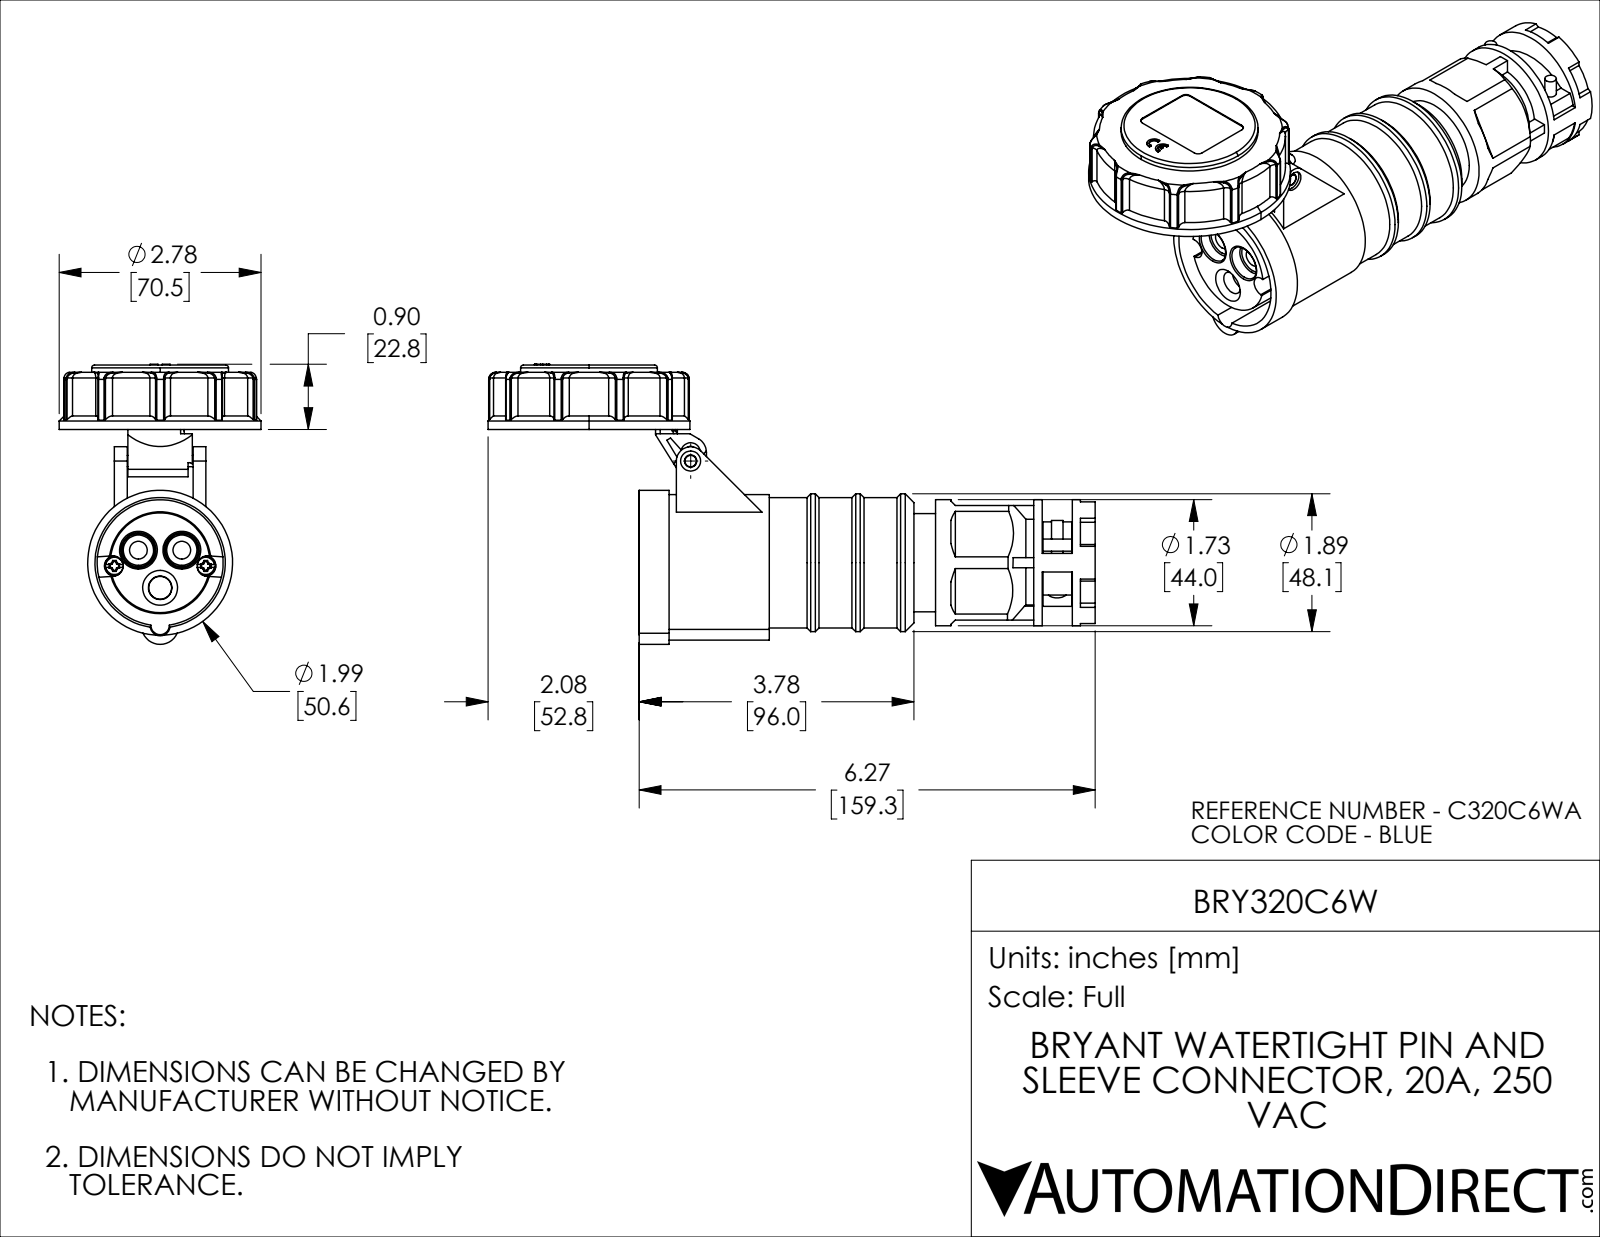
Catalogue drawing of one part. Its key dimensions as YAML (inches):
part_name: "BRY320C6W"
step_written_by: "SolidWorks 2021 (CONFIG_CONTROL_DESIGN)"
units: inches
bodies: {solids: 9, faces: 676, planar: 261, cylindrical: 247, other: 168}
overall_size: [8.349, 3.85, 2.776]
volume: 16.64
surface_area: 112.8
round_holes:
  - {diameter: 0.157, count: 2}
  - {diameter: 0.244, count: 2}
  - {diameter: 0.295, count: 2}
  - {diameter: 0.169, count: 1}
  - {diameter: 0.276, count: 1}
  - {diameter: 0.323, count: 1}
  - {diameter: 1.472, count: 1}
  - {diameter: 1.791, count: 1}
  - {diameter: 2.402, count: 1}
round_bosses_or_shafts:
  - {diameter: 2.776, count: 1}
  - {diameter: 1.992, count: 1}
  - {diameter: 1.894, count: 1}
  - {diameter: 1.882, count: 1}
  - {diameter: 1.874, count: 1}
  - {diameter: 1.791, count: 1}
  - {diameter: 1.732, count: 1}
  - {diameter: 1.35, count: 1}
partial_cylinders:
  - {radius: 0.098, count: 24}
  - {radius: 0.02, count: 20}
  - {radius: 0.039, count: 5}
  - {radius: 0.079, count: 4}
  - {radius: 0.069, count: 2}
  - {radius: 0.134, count: 2}
  - {radius: 0.14, count: 2}
  - {radius: 0.143, count: 2}
face_to_face_distances: [0.118, 2.343, 0.531, 0.522, 0.404, 0.669, 0.128, 0.413, 0.098, 1.575]
hole_center_spacings: [0.344, 0.596, 6.465, 0.597, 1.161]
